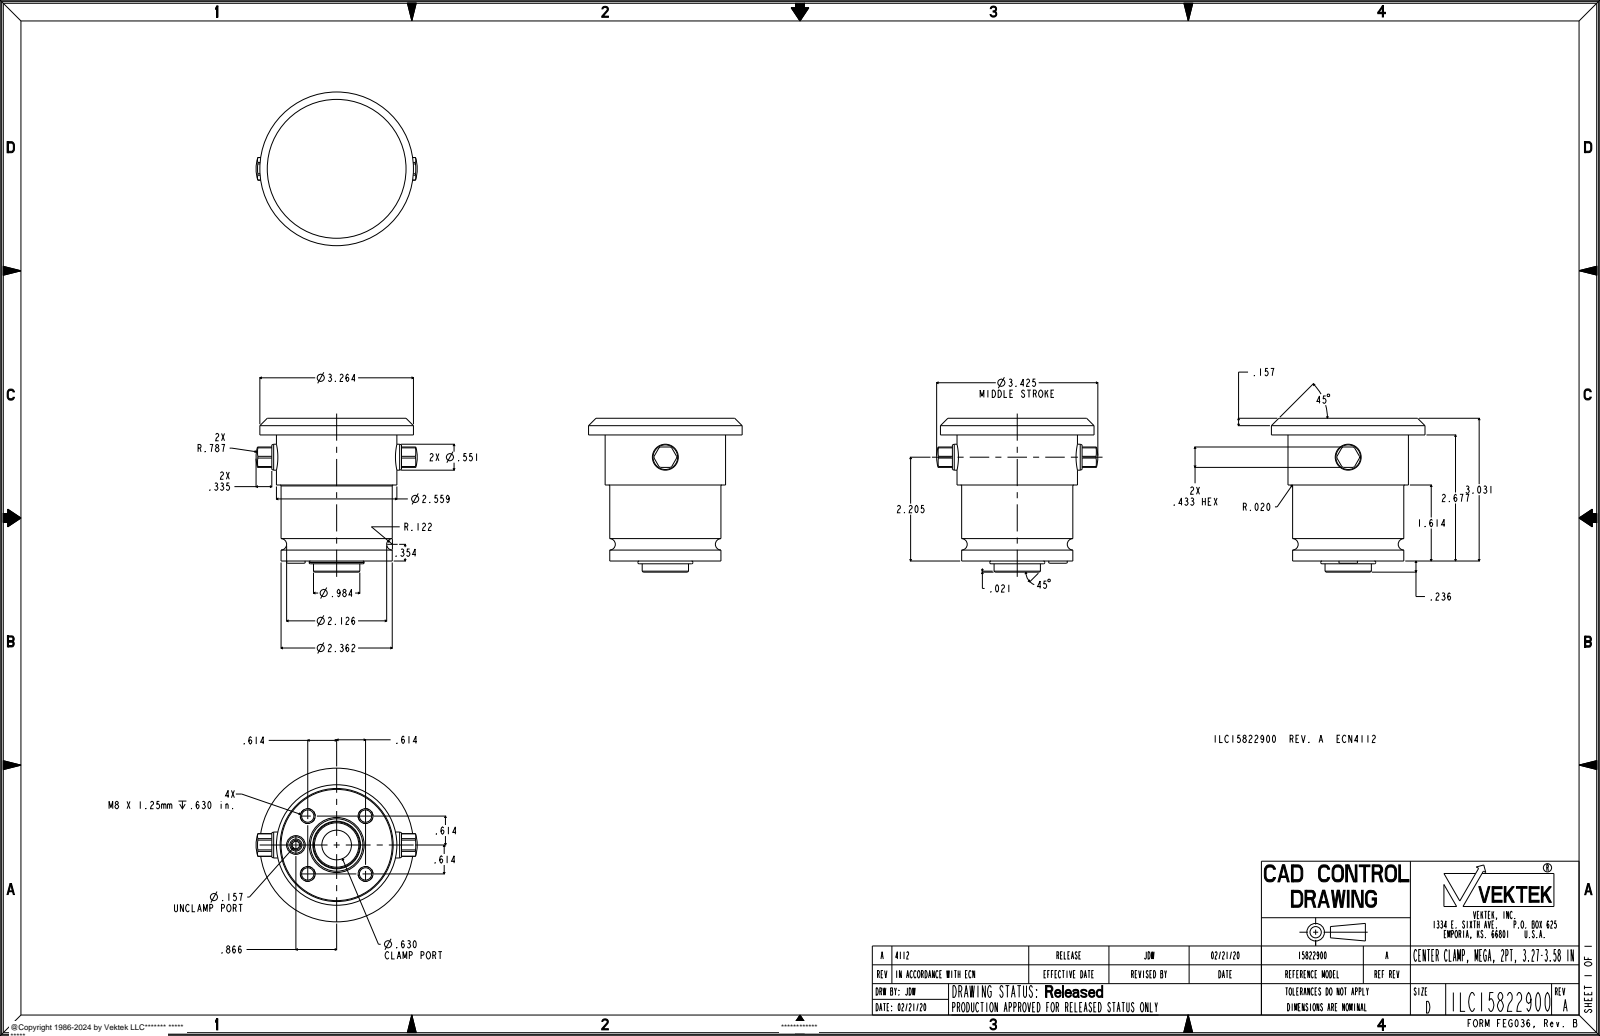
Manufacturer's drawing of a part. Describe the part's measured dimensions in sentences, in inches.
The part is named "ILC15822900". Its 3-D file was written by "PRO/ENGINEER BY PARAMETRIC TECHNOLOGY CORPORATION, 2013320 (AUTOMOTIVE_DESIGN)". It is 1 solid with 135 faces: 37 planar, 54 cylindrical and 44 other. Overall it measures 3.425 by 3.268 by 3.264 inches. Its volume is 15.33 cubic inches and its surface area 49.71 square inches. Round holes: 4 of diameter 0.262, 1 of diameter 0.157, 1 of diameter 0.551, 1 of diameter 0.63. Round bosses or shafts: 4 of diameter 0.315, 1 of diameter 3.264, 1 of diameter 2.559, 1 of diameter 2.362, 1 of diameter 1.169, 1 of diameter 0.984. Partial cylindrical surfaces (rounded edges, fillets, slot ends): 1 of radius 0.24. The main face-to-face distances are 3.031, 2.677, 0.354, 0.118, 1.614, 1.063, 1.417, 0.098, 1.083, 0.236. The hole center spacings are 0.869, 1.228, 0.664, 1.603, 1.737, 0.866.
